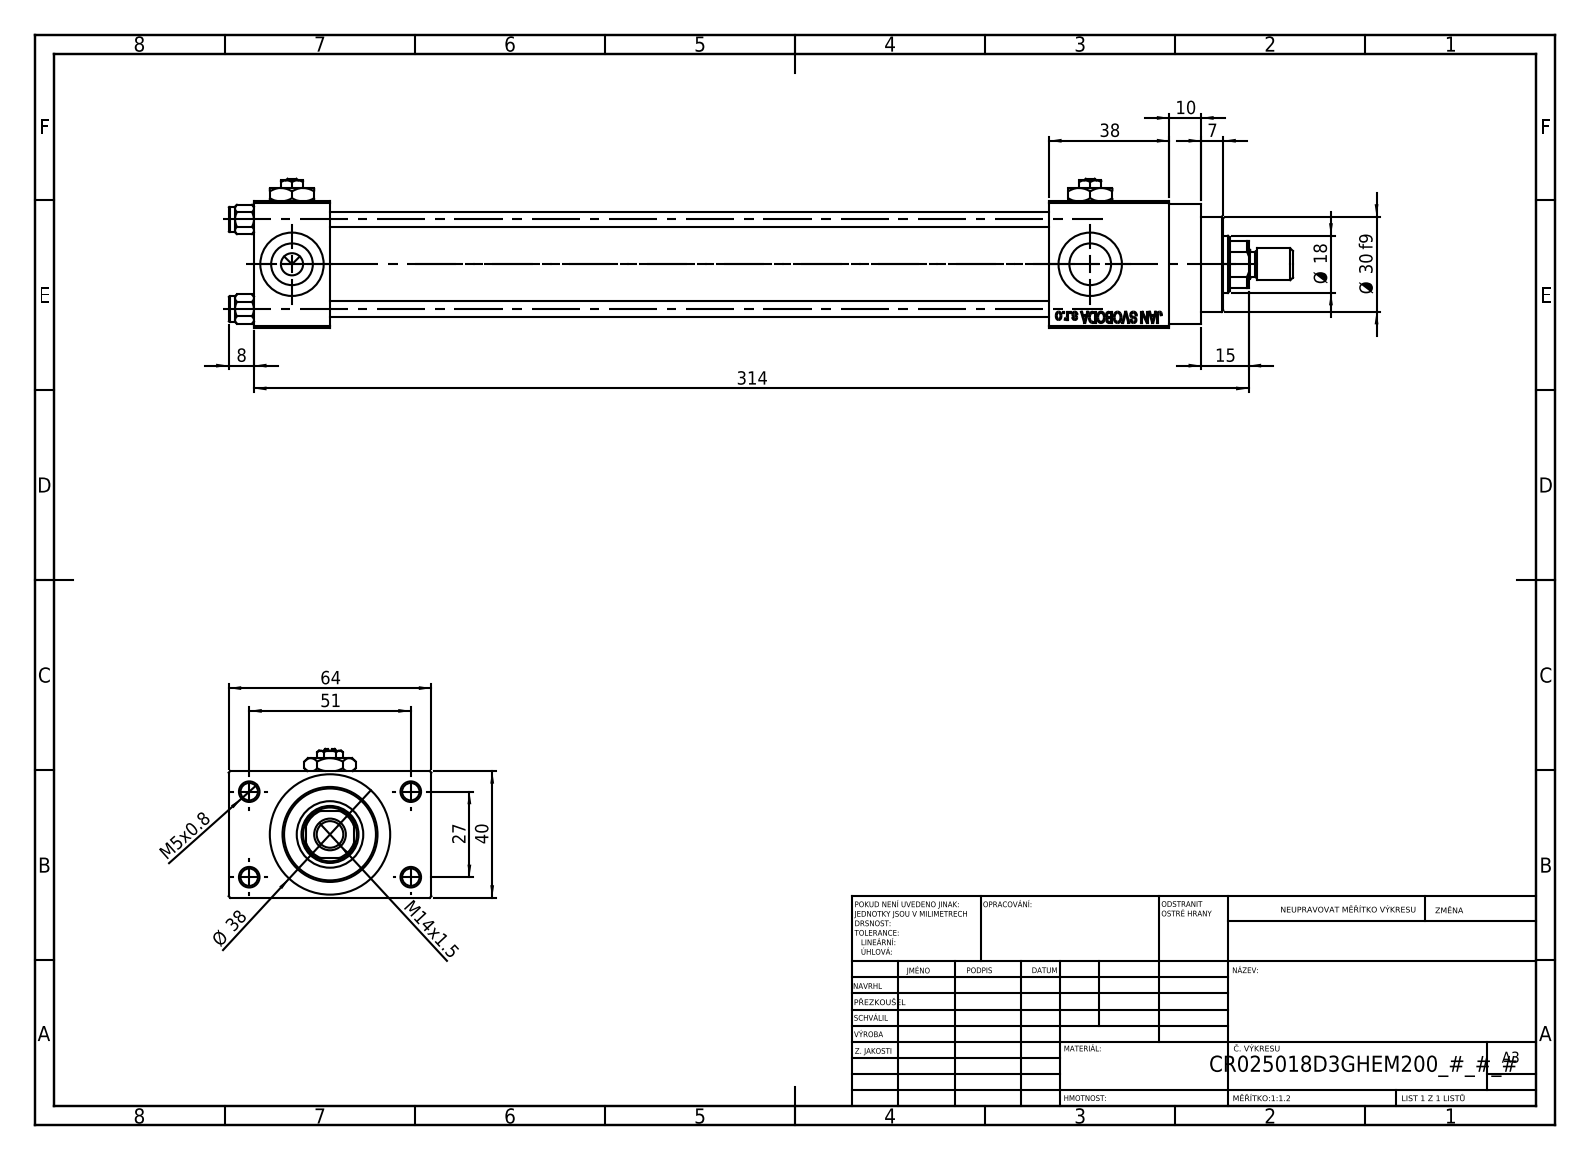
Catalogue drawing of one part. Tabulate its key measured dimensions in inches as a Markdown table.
| quantity | value |
| --- | --- |
| part name | NUT_M5_D; Zatka_pro_OIL_PORT; ROD_END_E; V215CR_D_TYCINKA (+3 more) |
| STEP written by | SolidWorks 2019 (CONFIG_CONTROL_DESIGN) |
| units | inches |
| bodies | 14 solids, 1212 faces (545 planar, 101 cylindrical, 566 other) |
| overall size | 13.228 × 2.52 × 1.85 |
| volume | 17.49 in³ |
| surface area | 186.2 in² |
| round holes (diameter × count) | 0.787 × 5, 0.197 × 4, 0.217 × 4, 0.518 × 4, 0.276 × 3, 0.335 × 1, 0.709 × 1, 0.827 × 1, 0.984 × 1, 1.181 × 1 |
| round bosses / shafts (diameter × count) | 0.315 × 5, 1.496 × 1, 1.22 × 1, 0.394 × 1 |
| partial cylindrical surfaces (radius × count) | 0.335 × 1 |
| main face-to-face distances | 1.575, 0.472, 8.937, 0.945, 9.882, 2.047, 1.496, 10.433, 11.378, 2.52 |
| hole center spacings | 0.448, 0.788, 1.114, 1.136, 1.177, 1.561, 1.903, 1.063 |
